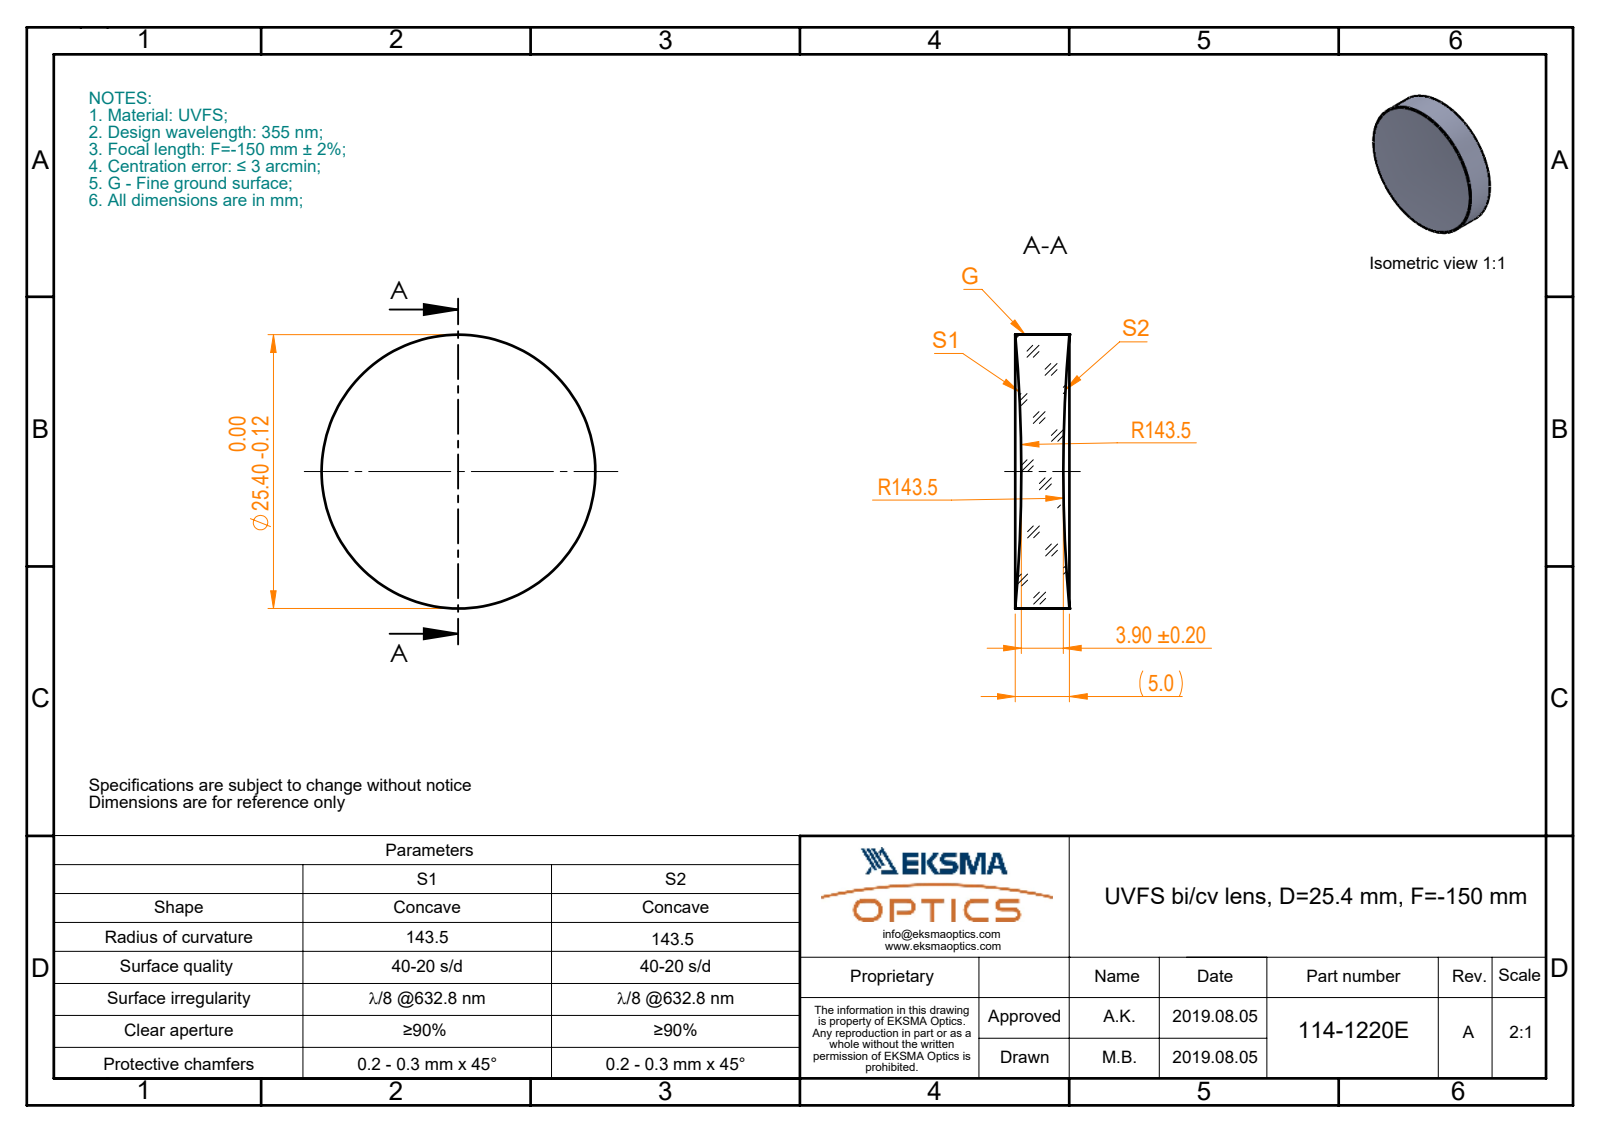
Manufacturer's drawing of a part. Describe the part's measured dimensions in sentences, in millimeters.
The part is named "114-1220E UVFS bi-cv 25.4 F-150". Its 3-D file was written by "SolidWorks 2017 (CONFIG_CONTROL_DESIGN)". It is 1 solid with 6 faces: 0 planar, 2 cylindrical and 4 other. Overall it measures 25.4 by 25.4 by 5.03 millimeters. Its volume is 2 261 cubic millimeters and its surface area 1 417 square millimeters. Round bosses or shafts: 1 of diameter 25.4.
